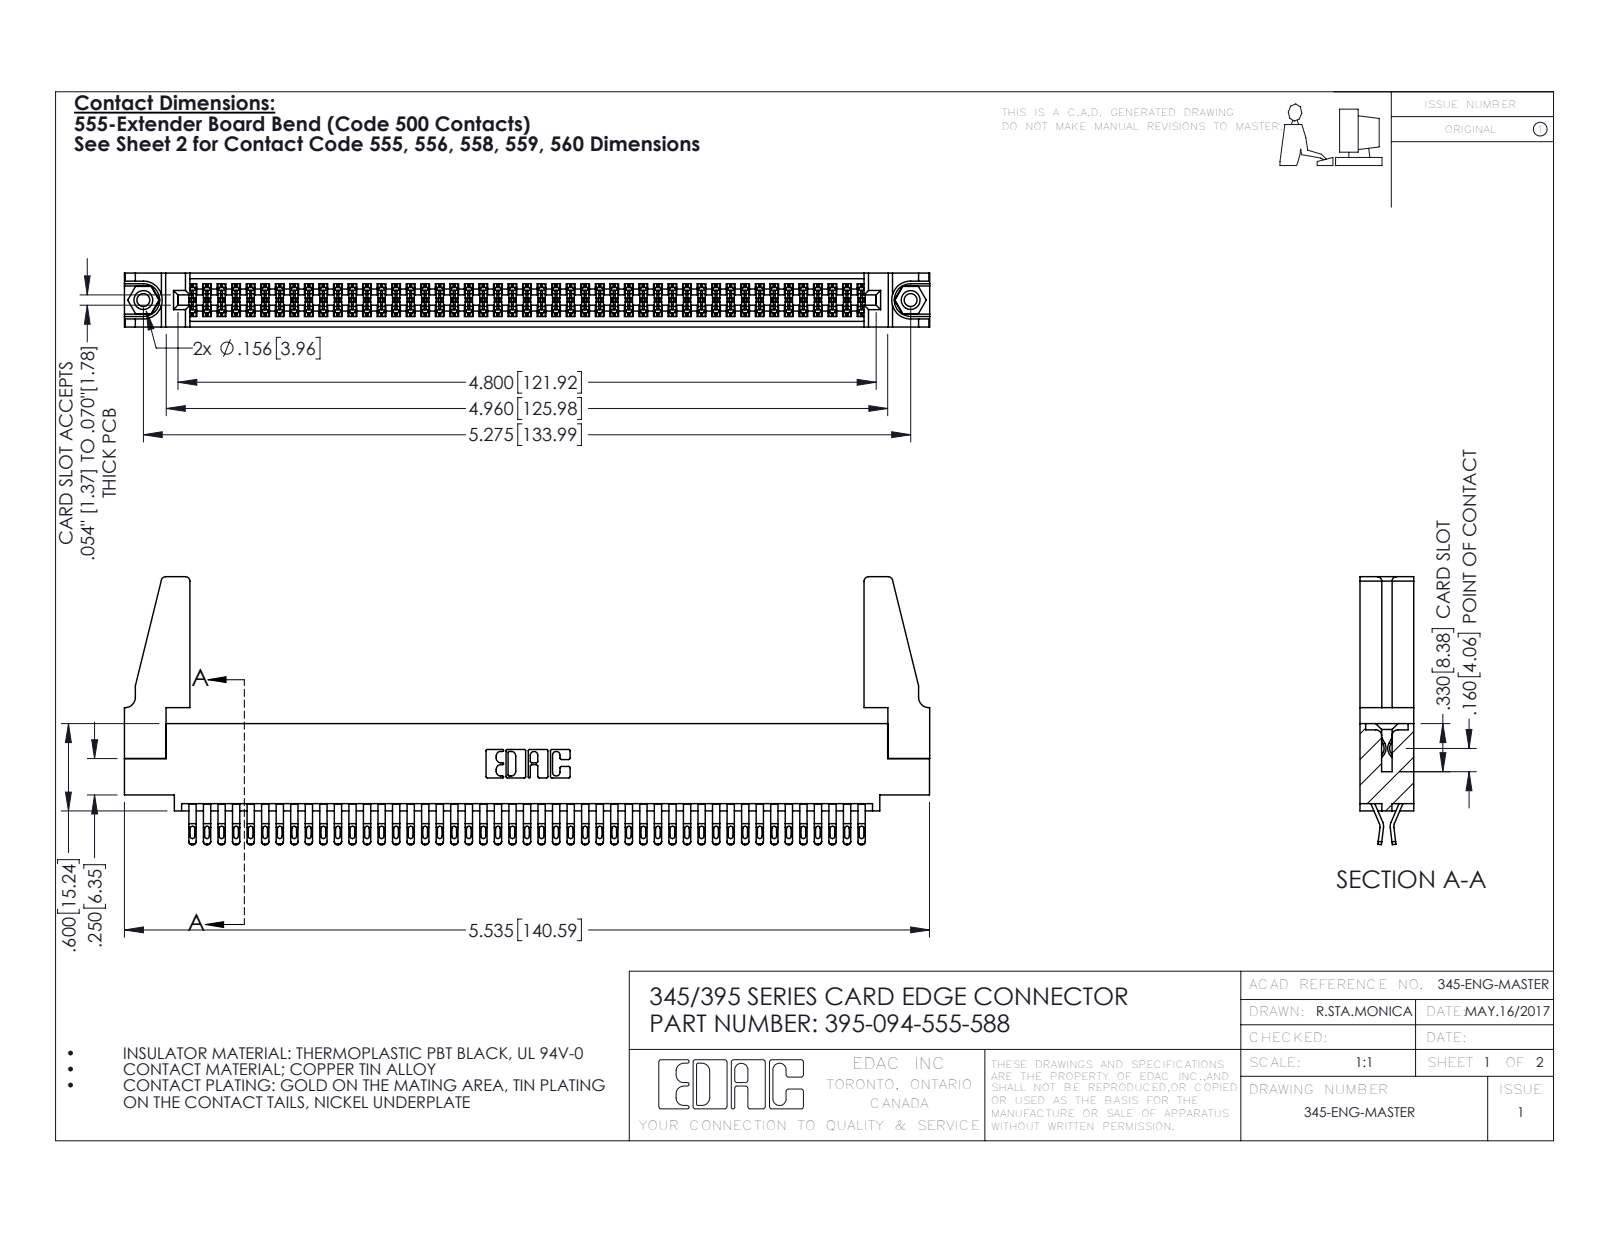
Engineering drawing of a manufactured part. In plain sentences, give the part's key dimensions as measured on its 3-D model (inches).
The part is named "345 Part_0.110 Offset - 0.156 Dia-TH; 395-094-555-588; 345-292-001_555 Tail; 345-220-078_345-220-088 (+1 more)". Its 3-D file was written by "SolidWorks 2016 (CONFIG_CONTROL_DESIGN)". It is 99 solids with 5518 faces: 3070 planar, 2432 cylindrical and 16 other. Overall it measures 5.536 by 1.842 by 0.37 inches. Its volume is 1.047 cubic inches and its surface area 38.46 square inches. Round holes: 2 of diameter 0.089, 2 of diameter 0.125, 2 of diameter 0.156, 1 of diameter 0.064. Round bosses or shafts: 2 of diameter 0.155. Partial cylindrical surfaces (rounded edges, fillets, slot ends): 235 of radius 0.016, 188 of radius 0.02, 141 of radius 0.006, 22 of radius 0.01, 8 of radius 0.03, 6 of radius 0.007, 6 of radius 0.031, 3 of radius 0.026. The main face-to-face distances are 0.072, 0.298, 0.37, 0.025, 0.2, 0.098, 0.272, 0.225, 0.175, 0.149. The hole center spacings are 0.27, 5.039, 5.275.
